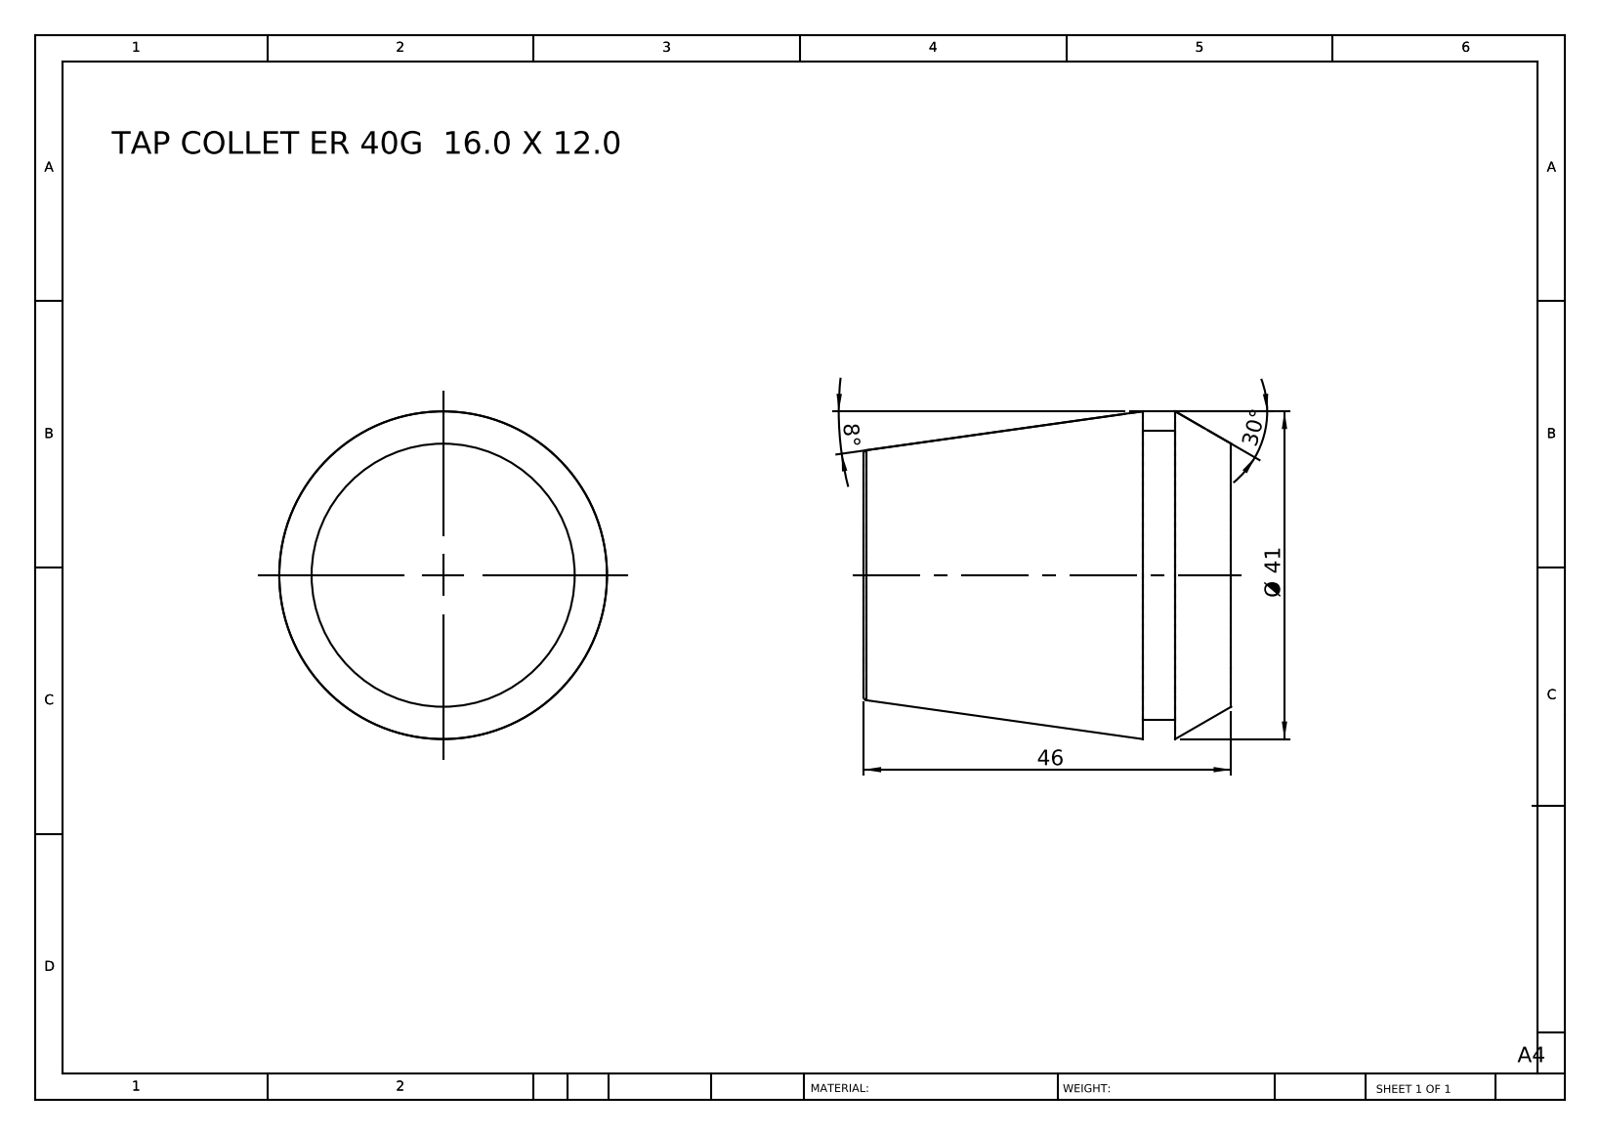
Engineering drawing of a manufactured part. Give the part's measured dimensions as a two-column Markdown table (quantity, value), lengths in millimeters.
| quantity | value |
| --- | --- |
| part name | TAP COLLET ER 40G 16.0 X 12.0 |
| STEP written by | SolidWorks 2014 (CONFIG_CONTROL_DESIGN) |
| units | millimeters |
| bodies | 1 solid, 12 faces (4 planar, 2 cylindrical, 6 other) |
| overall size | 46 × 41 × 41 |
| volume | 47 690 mm³ |
| surface area | 7 586 mm² |
| round bosses / shafts (diameter × count) | 36.2 × 1 |
| main face-to-face distances | 46, 11.1, 34.9, 7, 4.1, 39 |
